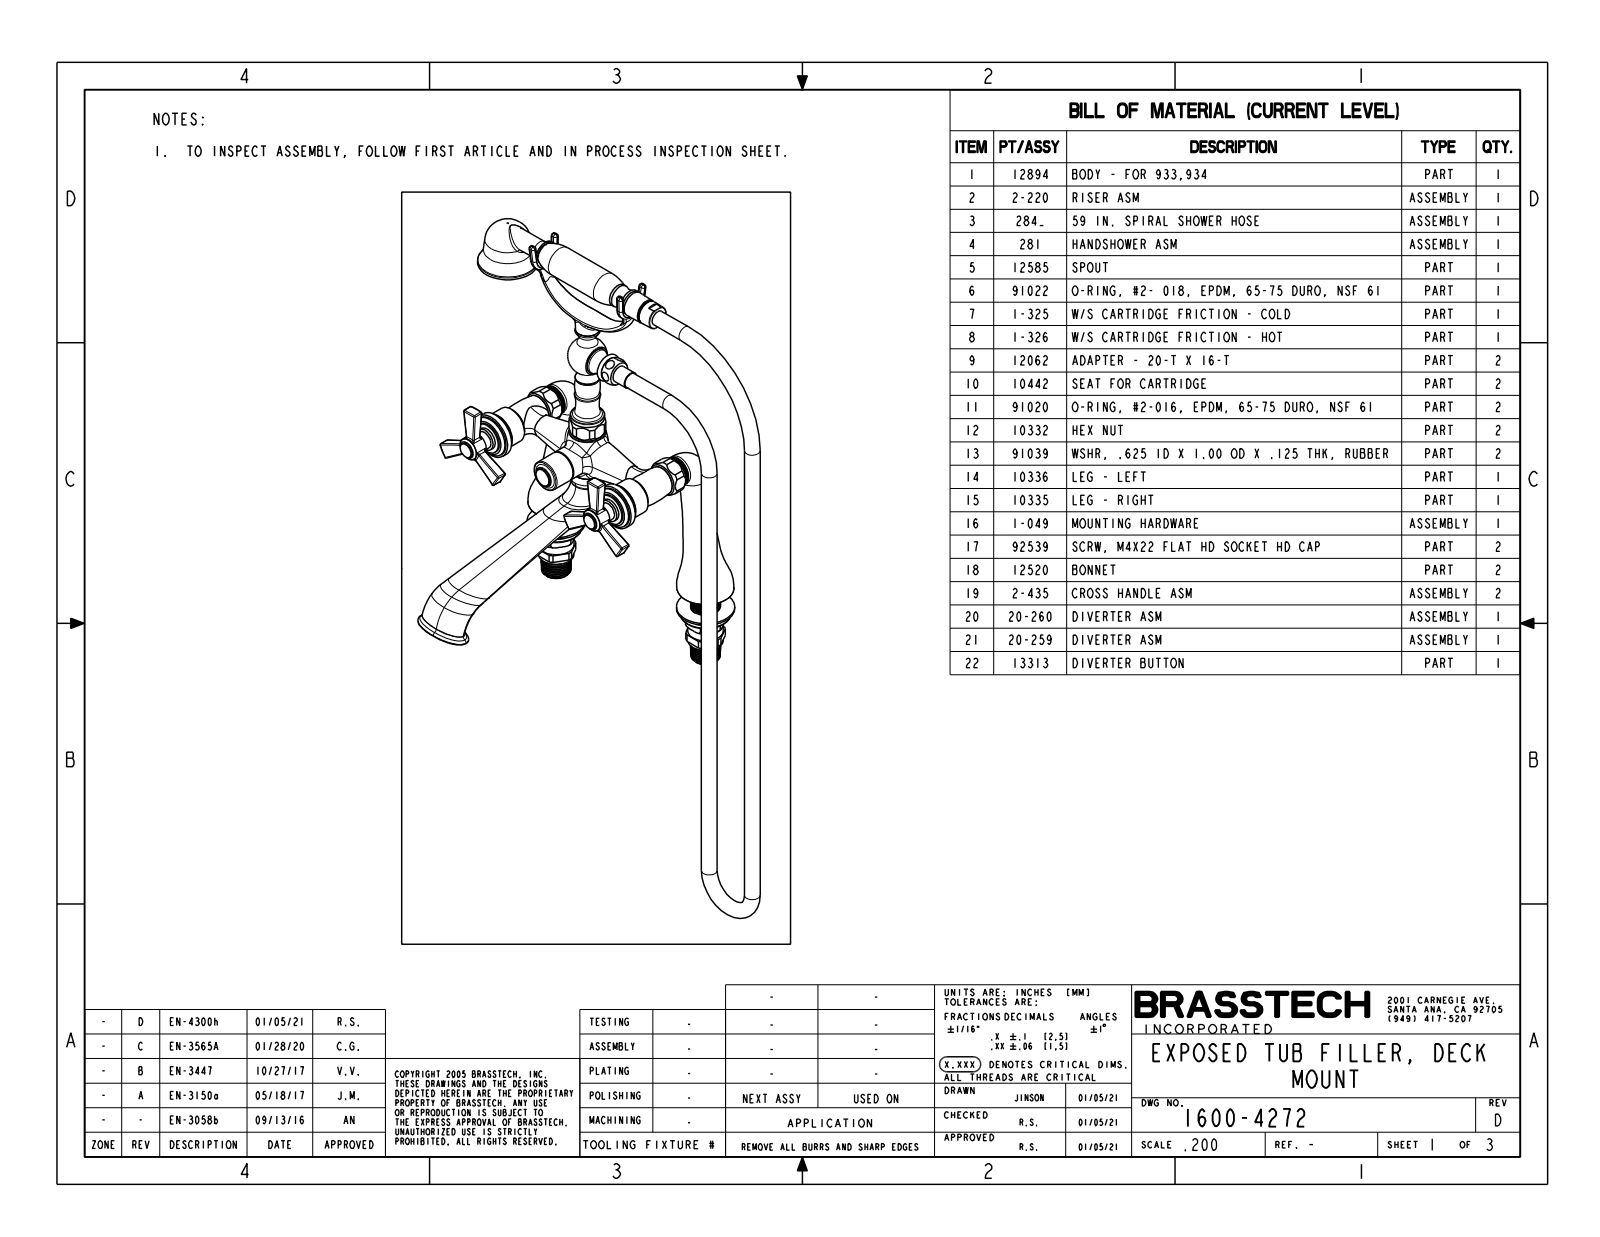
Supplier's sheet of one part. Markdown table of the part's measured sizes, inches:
| quantity | value |
| --- | --- |
| part name | 1600-4272 |
| STEP written by | CREO PARAMETRIC BY PTC INC, 2018400 (CONFIG_CONTROL_DESIGN) |
| units | inches |
| bodies | 1 solid, 990 faces (166 planar, 281 cylindrical, 543 other) |
| overall size | 23.86 × 13.181 × 10.575 |
| volume | 62.59 in³ |
| surface area | 304.1 in² |
| round holes (diameter × count) | 0.046 × 52 |
| round bosses / shafts (diameter × count) | 0.82 × 4, 0.54 × 4, 1.1 × 3, 1.6 × 2, 1.45 × 2, 1.3 × 2, 1.02 × 2, 0.8 × 2 |
| partial cylindrical surfaces (radius × count) | 0.085 × 32, 0.04 × 12, 0.1 × 12, 0.637 × 3, 0.595 × 2, 0.405 × 1, 0.406 × 1, 0.45 × 1 |
| main face-to-face distances | 1.188, 0.982, 3, 0.2, 0.15, 2.516, 4.188, 1.812, 11.04, 10.058 |
| hole center spacings | 0.187, 0.367, 0.535, 0.813, 1.021, 0.184, 0.601, 0.685 |
